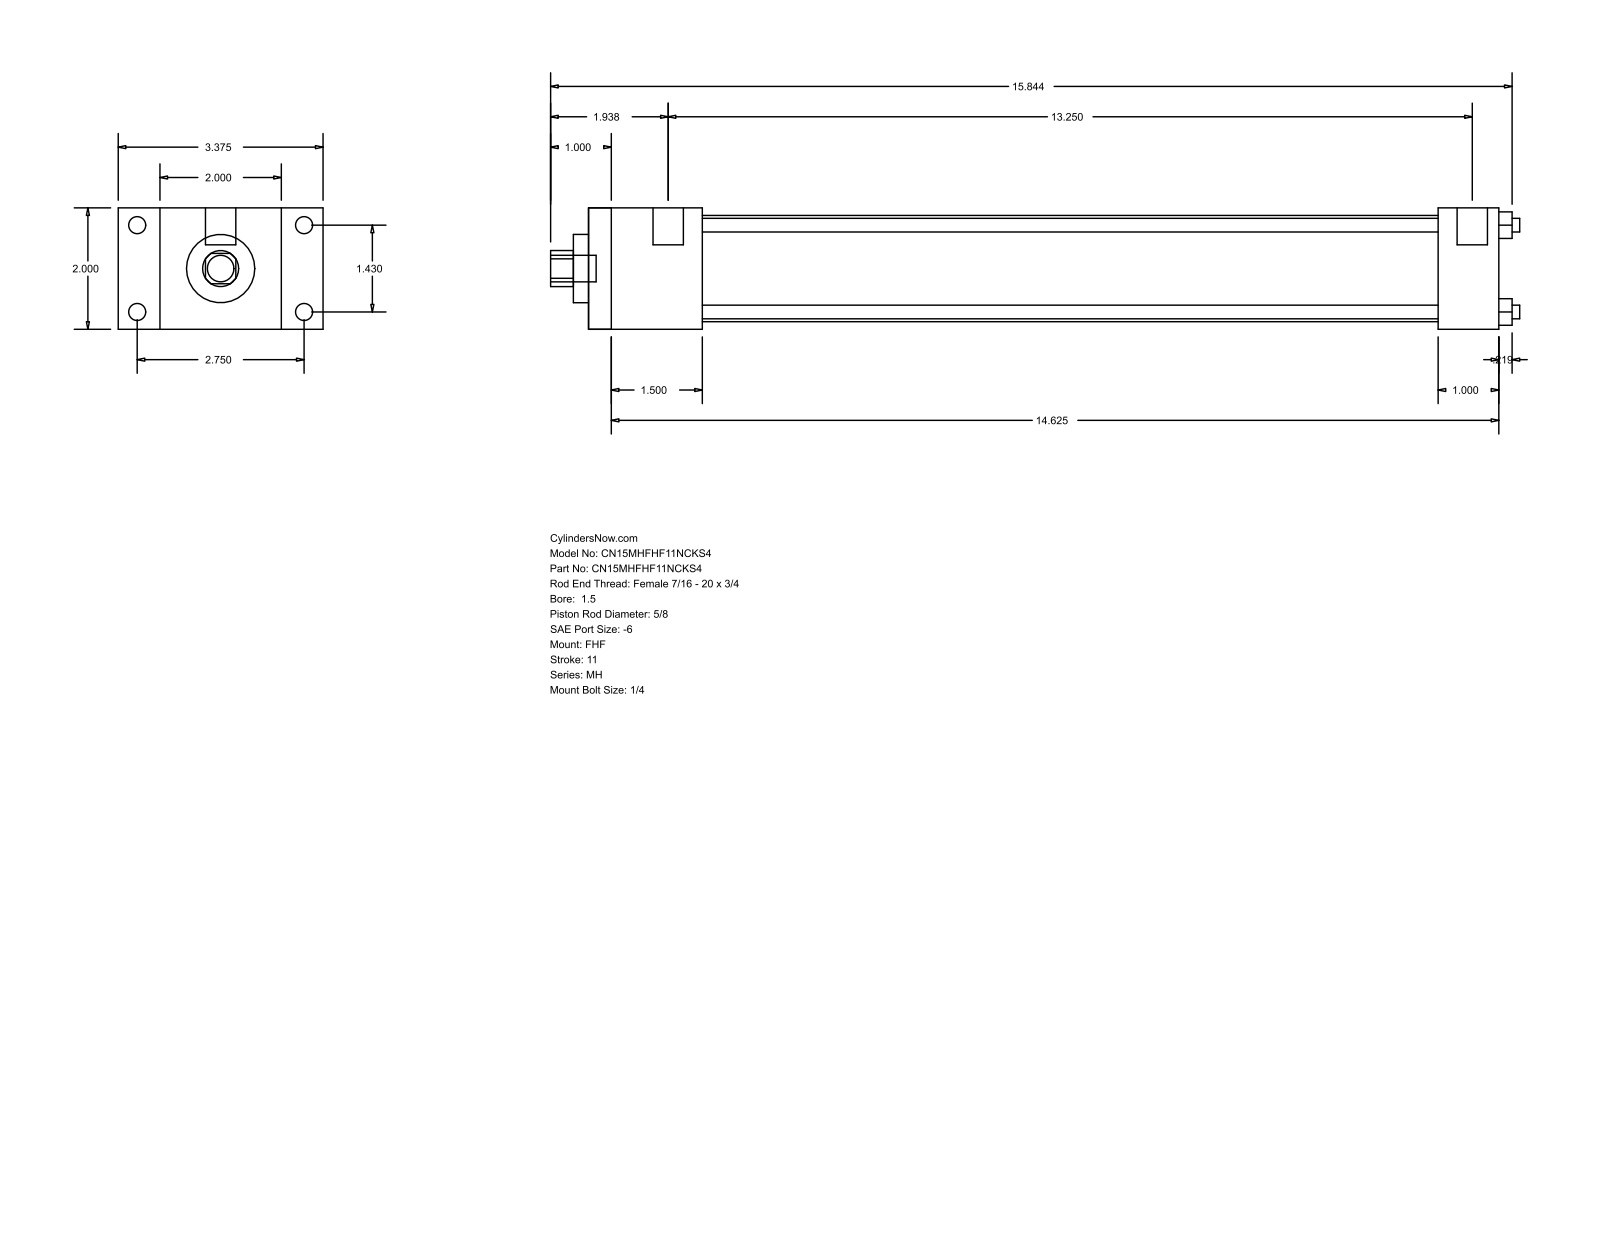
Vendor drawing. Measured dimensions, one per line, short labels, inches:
name: MH_FHF__0150_0.625
written by: GSSL Pune (CONFIG_CONTROL_DESIGN)
unit: in
bodies: 0 solids, 88 faces (60 planar, 28 cylindrical, 0 other)
size: 15.969 × 3.375 × 2
holes: 4× ⌀0.225, 1× ⌀0.625, 1× ⌀1.125, 1× ⌀1.75
bosses: 4× ⌀0.281, 4× ⌀0.219, 2× ⌀0.5, 1× ⌀0.437
rounds: 1× R0.297
face distances: 2, 0.687, 2.687, 1.875, 3.375, 15, 13.125, 14, 12.125, 1
hole spacings: 1.011, 1.43, 2.022
